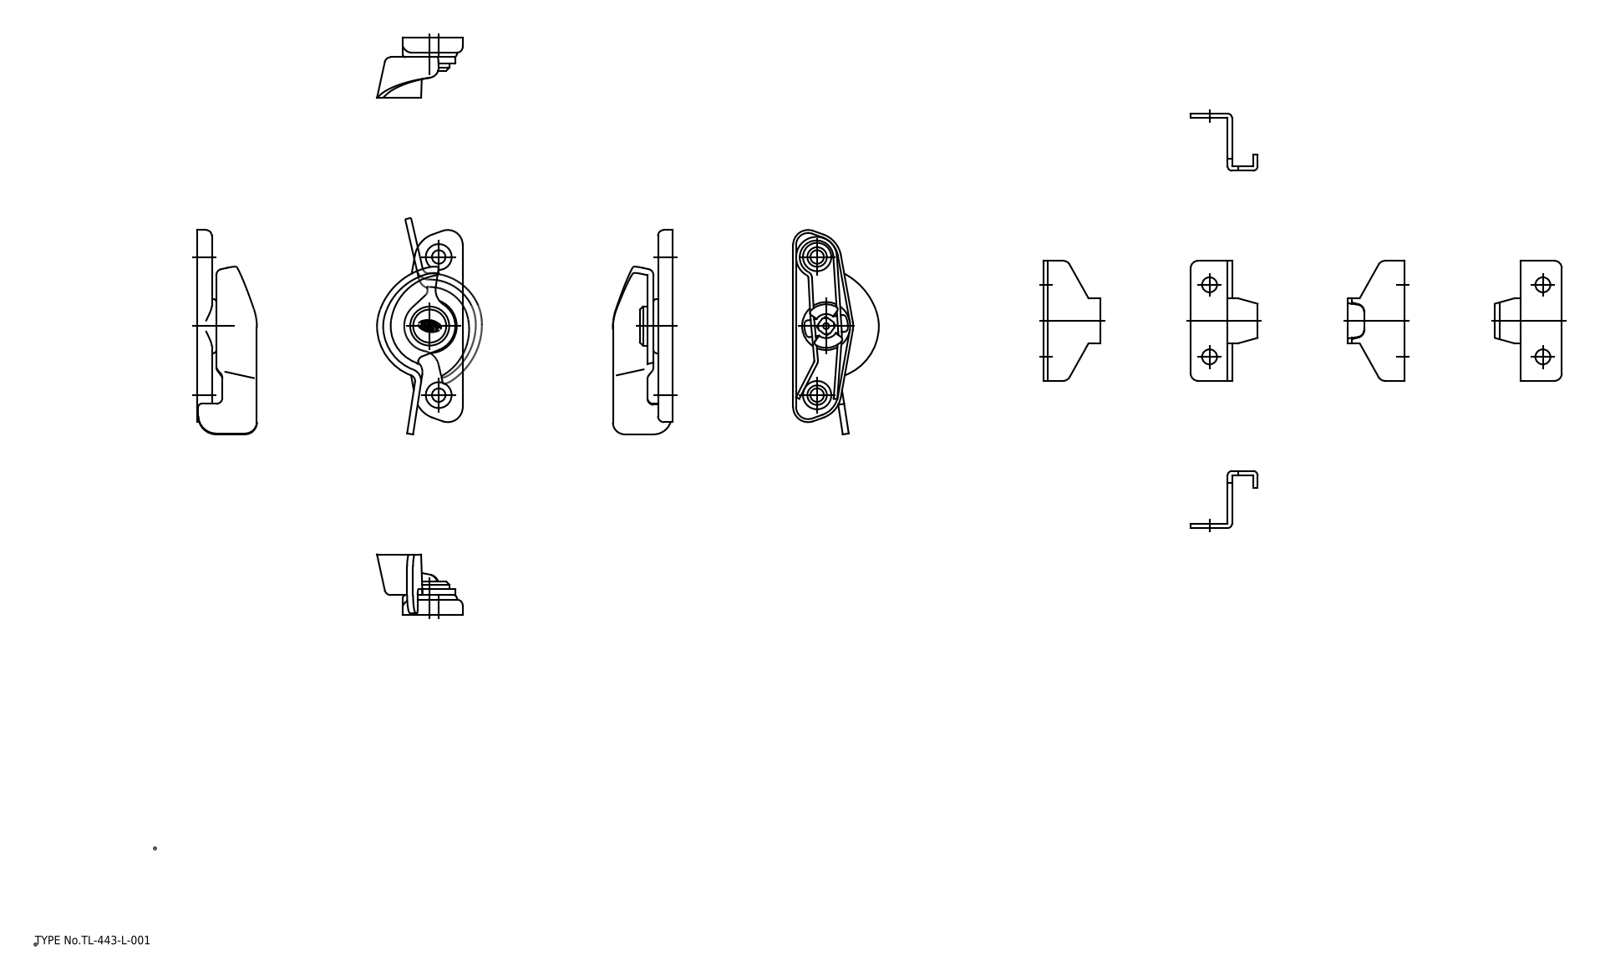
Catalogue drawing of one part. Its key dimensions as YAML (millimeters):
part_name: "レバー; ベース; スプリング; キーパー"
step_written_by: "spGate 19.8.4 (****-****-****-****) (AUTOMOTIVE_DESIGN)"
units: millimeters
bodies: {solids: 4, faces: 216, planar: 78, cylindrical: 72, other: 66}
overall_size: [68.08, 53.35, 20]
volume: 6494
surface_area: 9638
round_holes:
  - {diameter: 5, count: 2}
  - {diameter: 9.3, count: 1}
  - {diameter: 16, count: 1}
round_bosses_or_shafts:
  - {diameter: 1.2, count: 5}
  - {diameter: 18, count: 1}
  - {diameter: 13, count: 1}
partial_cylinders:
  - {radius: 1, count: 14}
  - {radius: 2, count: 7}
  - {radius: 2.5, count: 4}
  - {radius: 4, count: 4}
  - {radius: 1.5, count: 3}
  - {radius: 5, count: 3}
  - {radius: 6, count: 2}
  - {radius: 8, count: 2}
face_to_face_distances: [1.5, 1, 2.5, 4, 5.5, 3, 2, 4.5, 6, 13.5]
hole_center_spacings: [31.85, 24]
